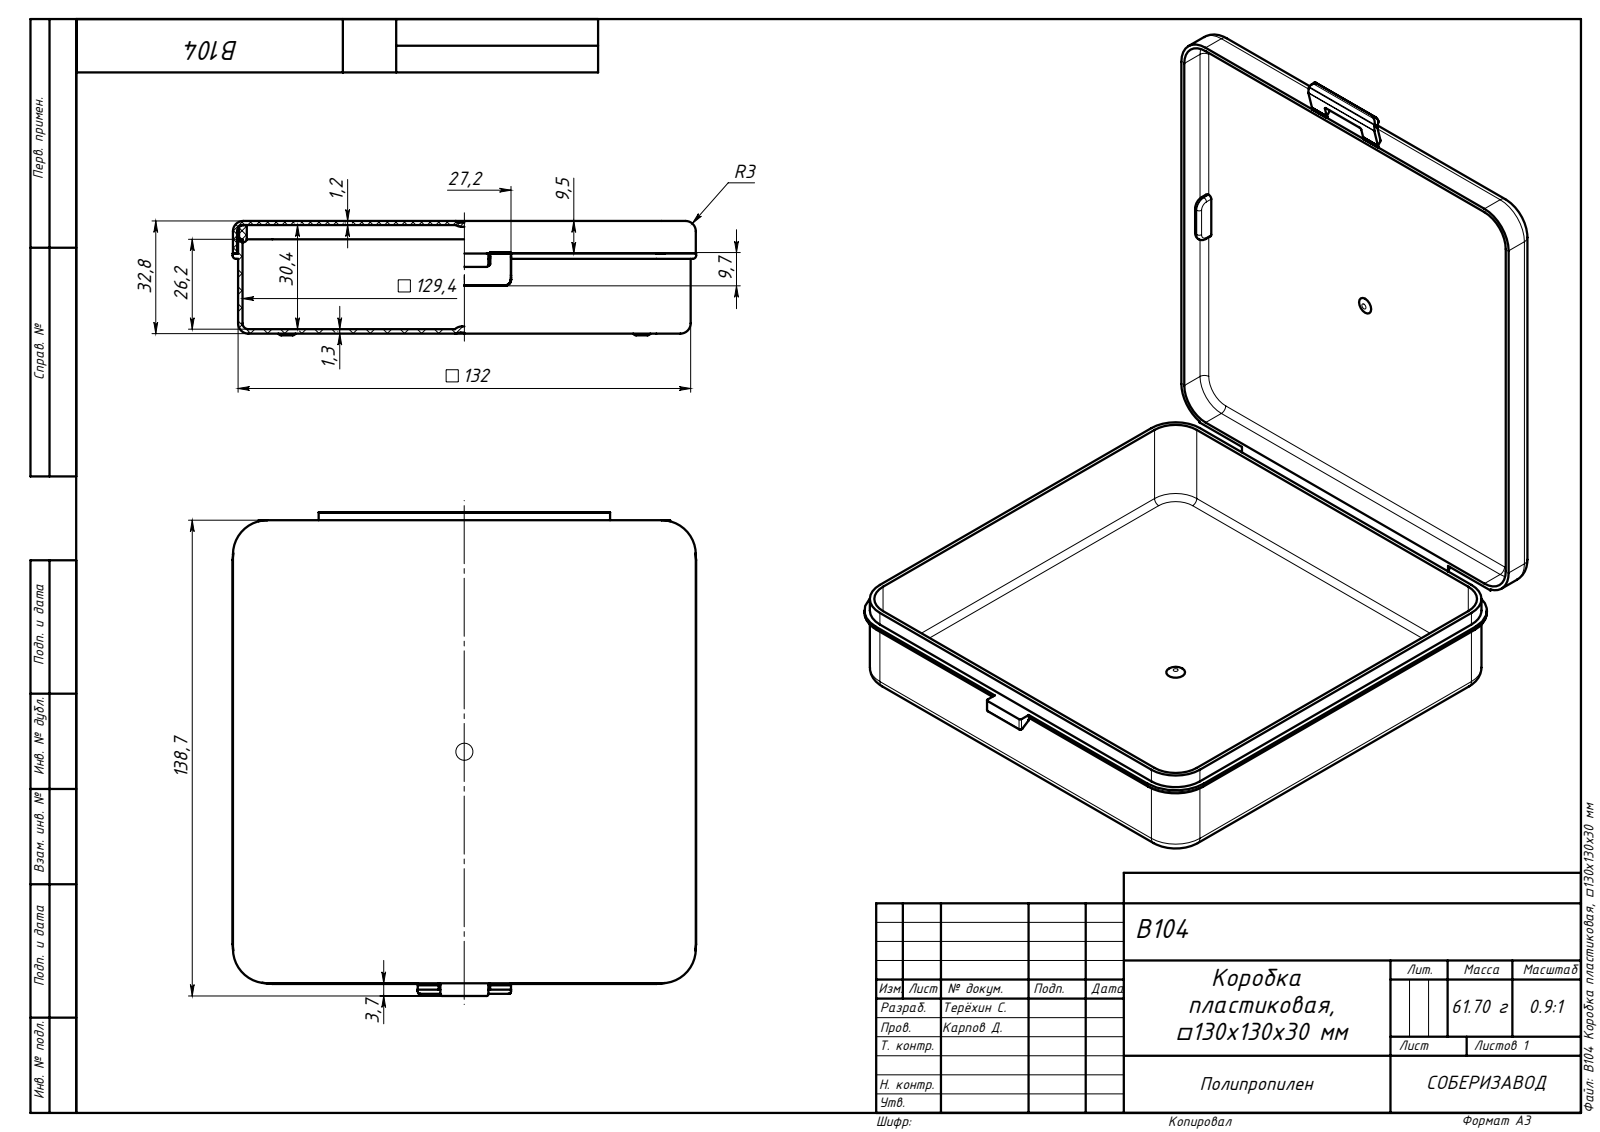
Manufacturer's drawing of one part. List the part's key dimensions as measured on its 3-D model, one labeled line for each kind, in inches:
Part name (STEP PRODUCT): B104 Защёлка_00; B104 Емкость_00; B104 Коробка пластиковая, ?130x130x30 мм; B104 Крышка_12
STEP written by: SolidWorks 2019 (AUTOMOTIVE_DESIGN)
Units: inches
Bodies: 12 solids, 307 faces (136 planar, 117 cylindrical, 54 other)
Overall size (bounding box): 5.549 × 5.323 × 1.313
Volume: 4.147 in³ · Surface area: 169.6 in²
Partial cylindrical surfaces — rounded edges, fillets, slot ends (radius × count): R0.039 ×20, R0.02 ×19, R0.118 ×10, R0.394 ×8, R0.028 ×7, R0.067 ×4, R0.071 ×4, R0.343 ×4
Main face-to-face distances: 0.051, 0.047, 1.195, 1.242, 1.293, 1.246, 5.146, 5.094, 5.197, 5.268
